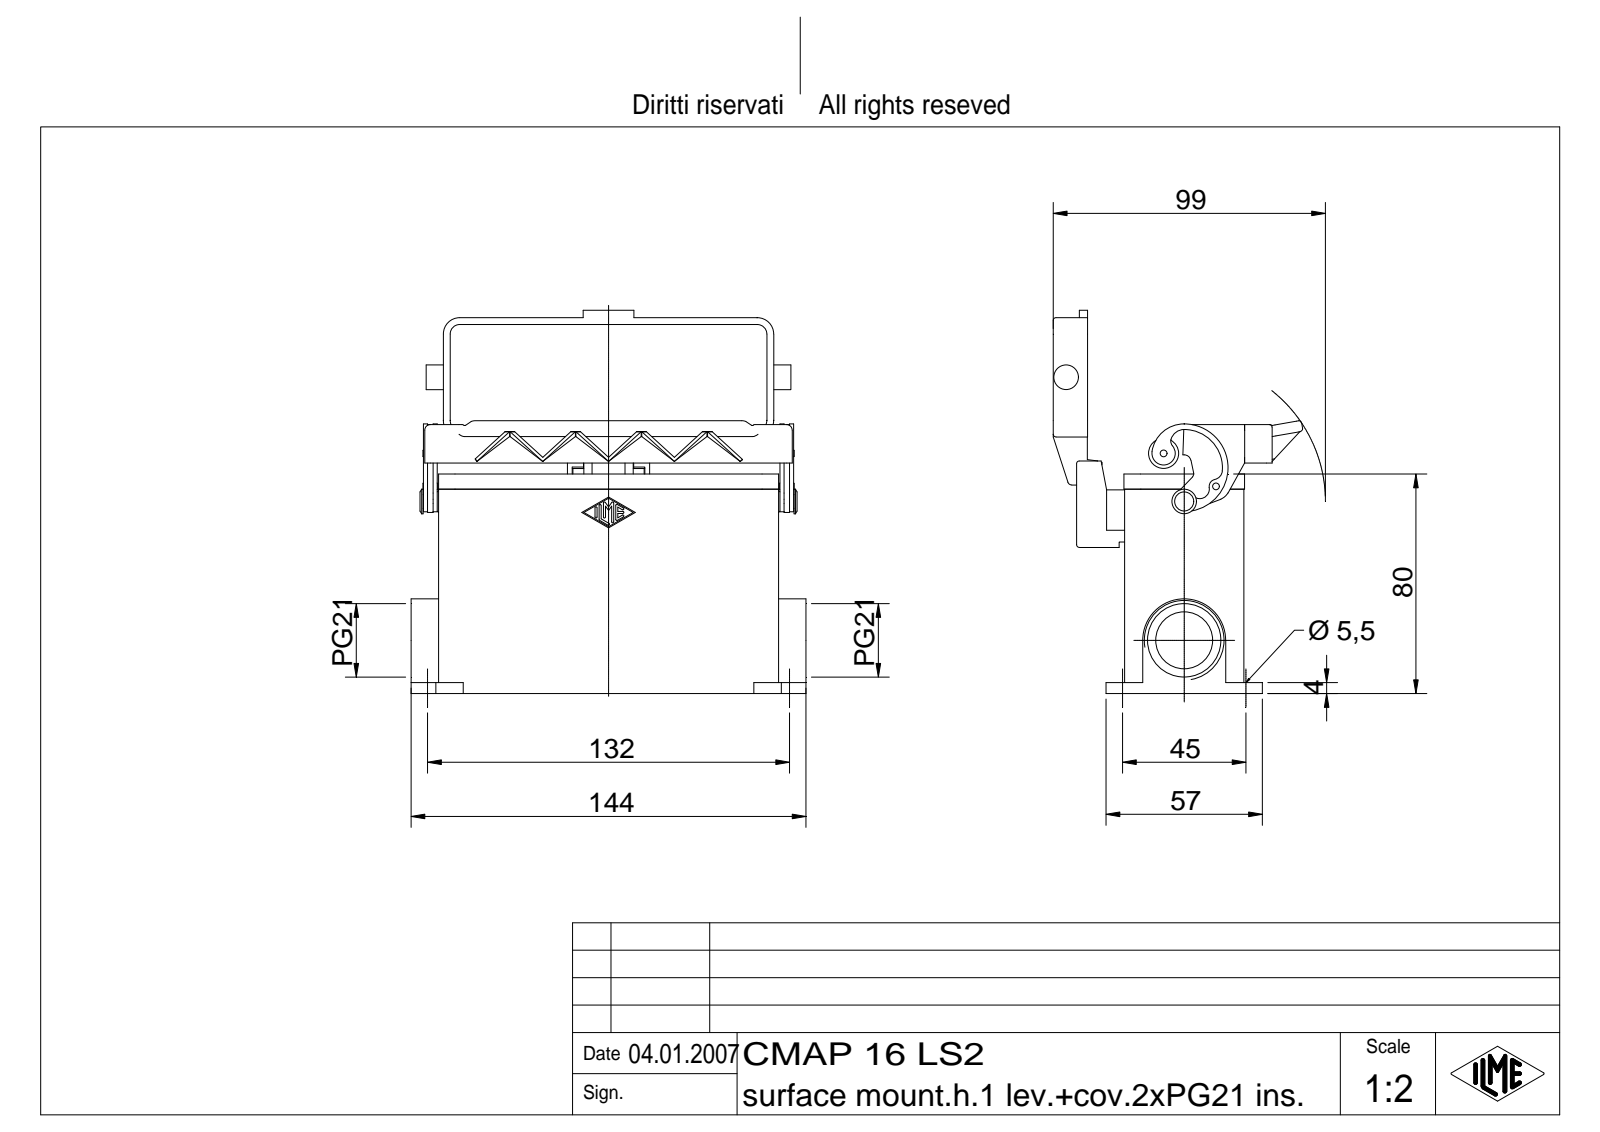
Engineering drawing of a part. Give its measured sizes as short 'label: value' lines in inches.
name: CMAP 16 LS2
written by: Autodesk Inventor 7 (AUTOMOTIVE_DESIGN)
unit: in
bodies: 6 solids, 623 faces (279 planar, 180 cylindrical, 164 other)
size: 5.669 × 5.5 × 3.581
volume: 11.74 in³; area: 165 in²
holes: 4× ⌀0.217, 1× ⌀0.079, 1× ⌀0.157, 1× ⌀0.818, 1× ⌀1.054
bosses: 2× ⌀0.354, 2× ⌀0.197, 1× ⌀0.433, 1× ⌀0.276, 1× ⌀0.157, 1× ⌀0.118, 1× ⌀0.098
rounds: 18× R0.039, 14× R0.015, 12× R0.079, 12× R0.236, 6× R0.059, 6× R0.138, 4× R0.118, 3× R0.02
face distances: 0.118, 1.594, 1.713, 0.157, 1.476, 1.024, 2.618, 2.736, 1.142, 1.004
hole spacings: 1.772, 5.197, 5.491, 2.256
